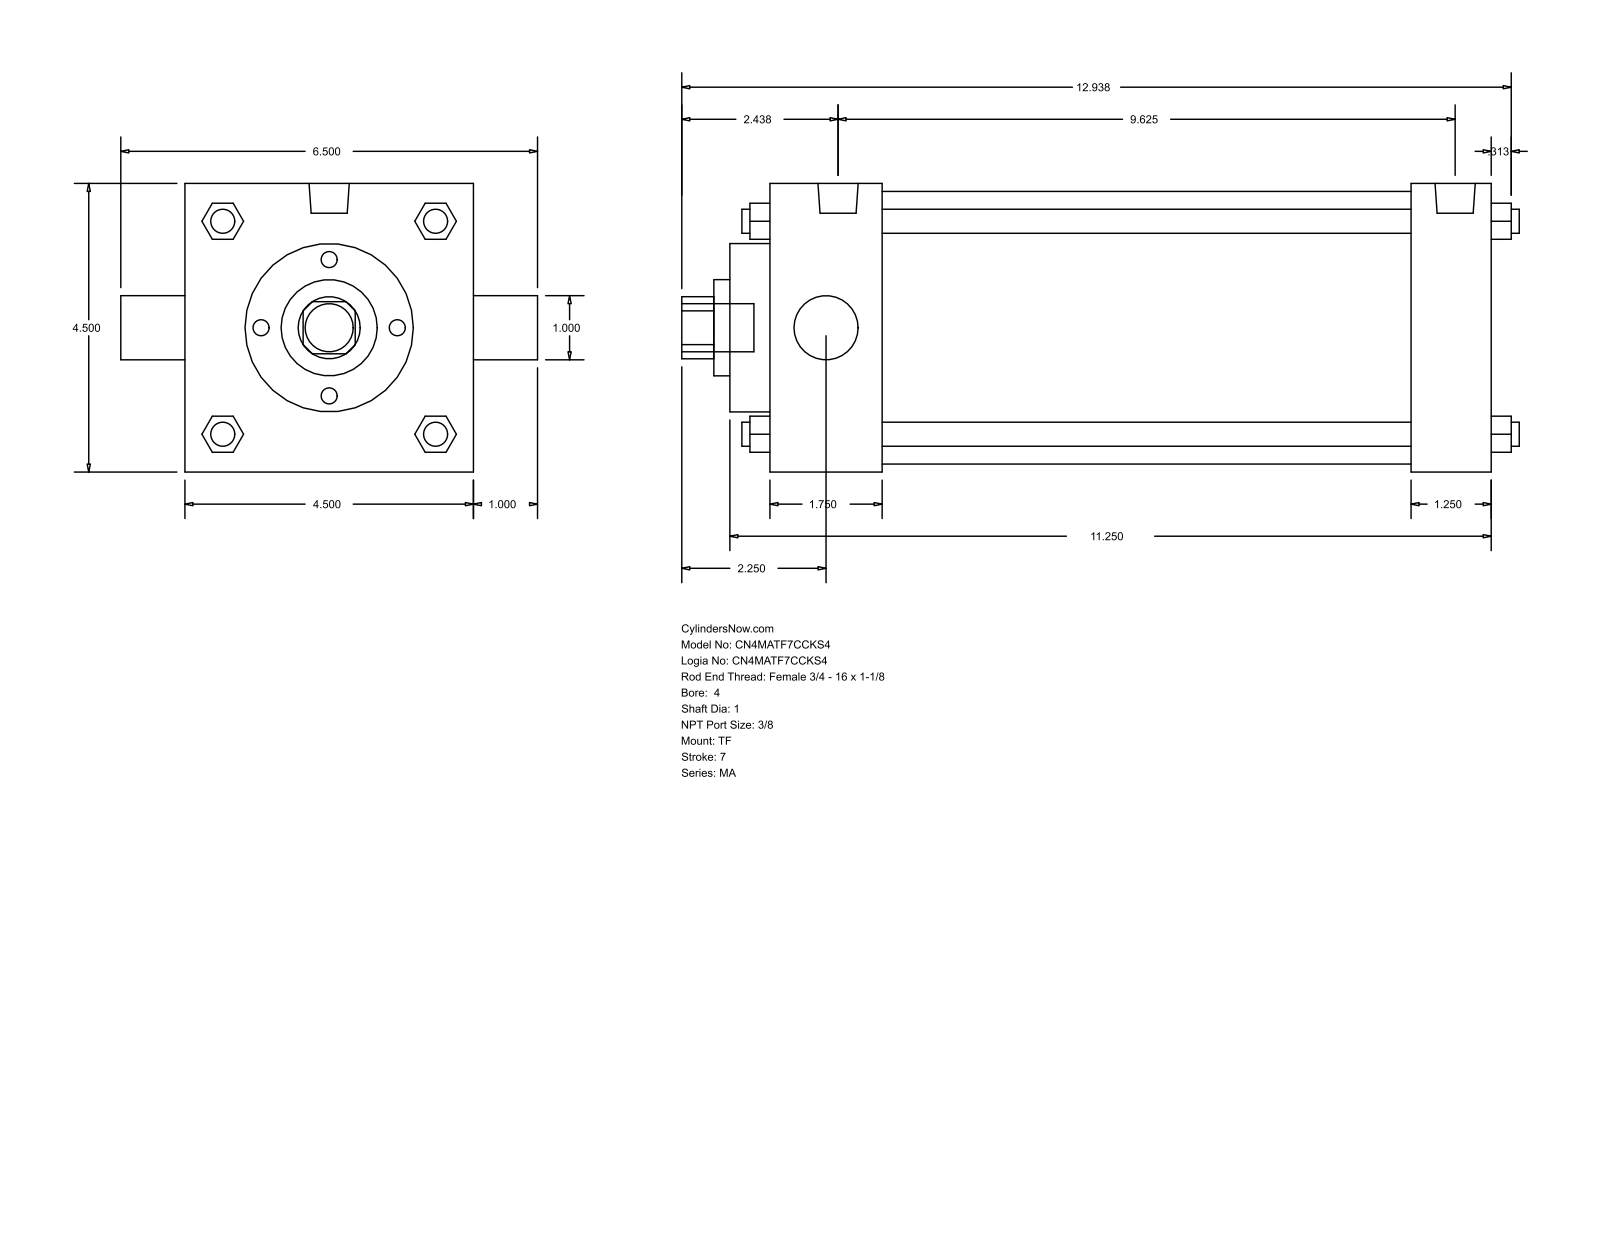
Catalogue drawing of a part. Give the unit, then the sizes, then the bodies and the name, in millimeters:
Units: millimetres
Overall size (bounding box): 331.79 × 165.1 × 114.3
Round holes (diameter × count): ⌀25.4 ×2, ⌀38.1 ×1, ⌀66.67 ×1, ⌀107.95 ×1
Round bosses / shafts (diameter × count): ⌀9.53 ×4, ⌀11.11 ×3, ⌀15.93 ×2, ⌀19.05 ×1
Partial cylindrical surfaces — rounded edges, fillets, slot ends (radius × count): R12.29 ×1
Main face-to-face distances: 114.3, 285.76, 254.01, 31.75, 44.46, 209.55, 241.3, 15.87, 60.33, 269.88
Bodies: 0 solids, 122 faces (93 planar, 29 cylindrical, 0 other)
Part name (STEP PRODUCT): MA_TF__0400_1
STEP written by: GSSL Pune (CONFIG_CONTROL_DESIGN)
